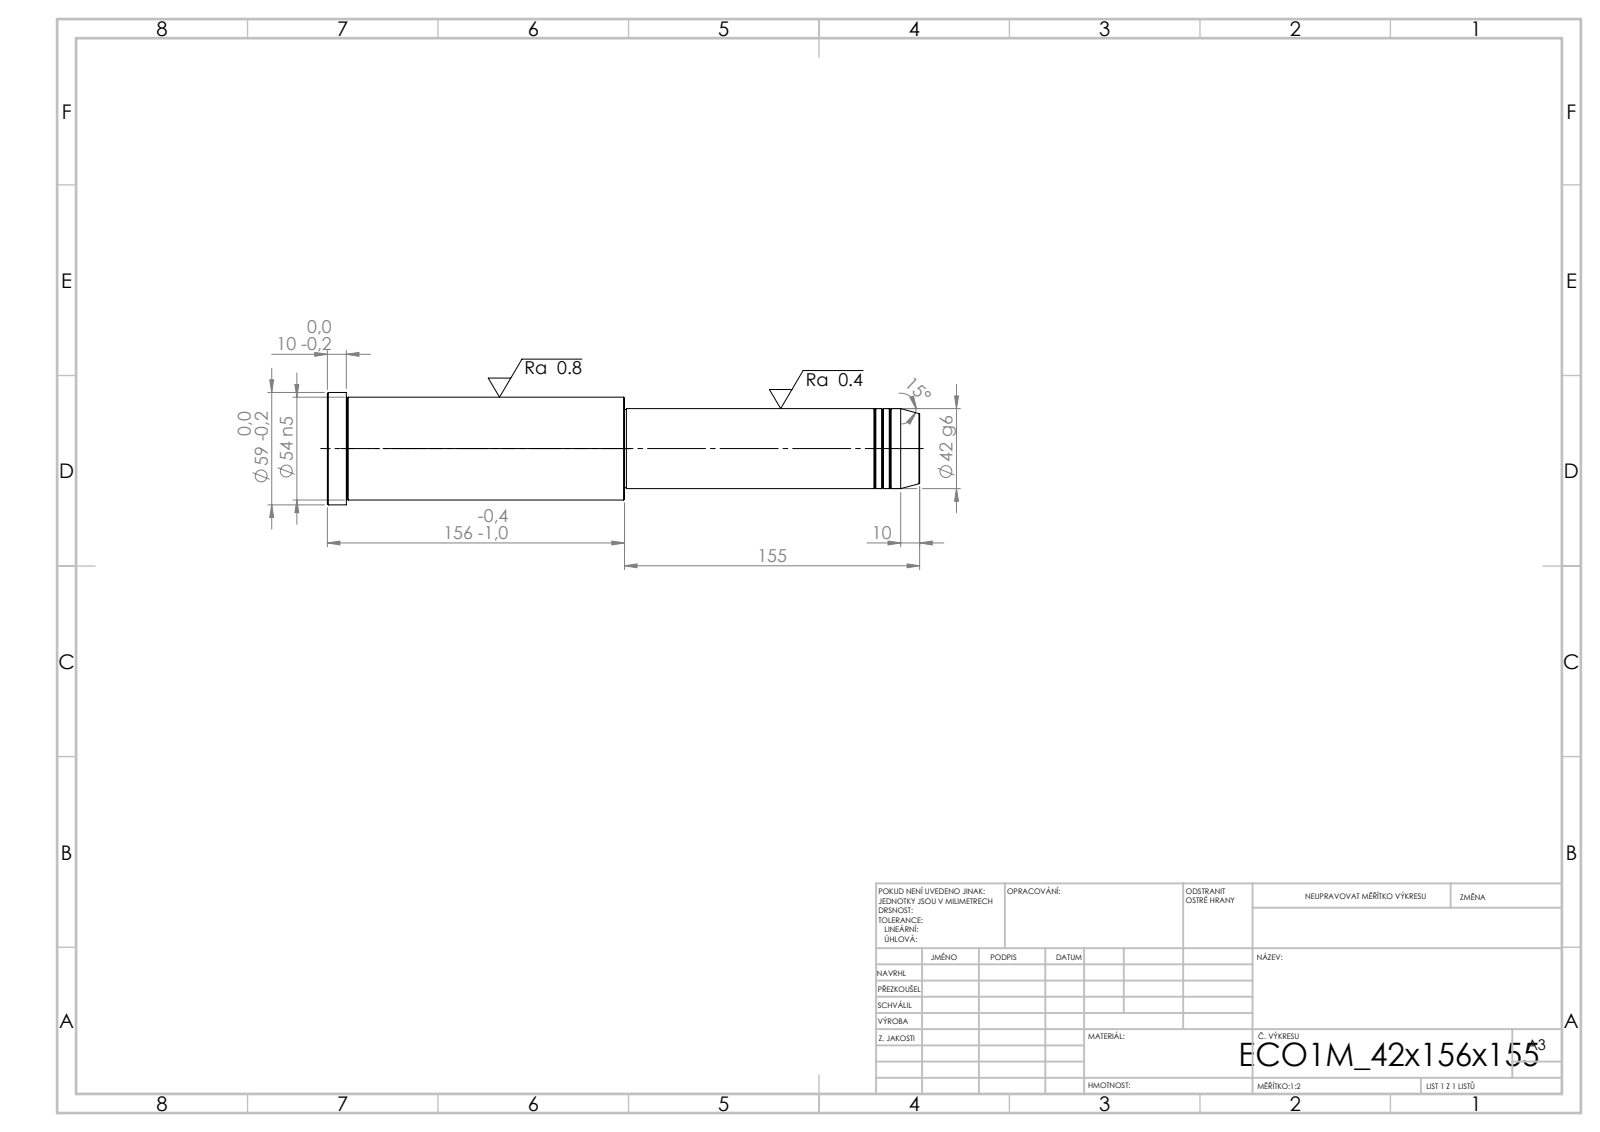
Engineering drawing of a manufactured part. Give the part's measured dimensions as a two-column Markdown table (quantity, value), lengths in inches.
| quantity | value |
| --- | --- |
| STEP written by | SolidWorks 2019 (CONFIG_CONTROL_DESIGN) |
| units | inches |
| bodies | 1 solid, 43 faces (5 planar, 14 cylindrical, 24 other) |
| overall size | 12.244 × 2.323 × 2.323 |
| volume | 35.05 in³ |
| surface area | 81.36 in² |
| round bosses / shafts (diameter × count) | 2.323 × 1, 2.126 × 1, 1.654 × 1, 1.614 × 1 |
| main face-to-face distances | 12.244, 6.102, 6.142, 11.85, 5.748, 0.394, 6.063, 0.039, 5.787, 6.181 |
